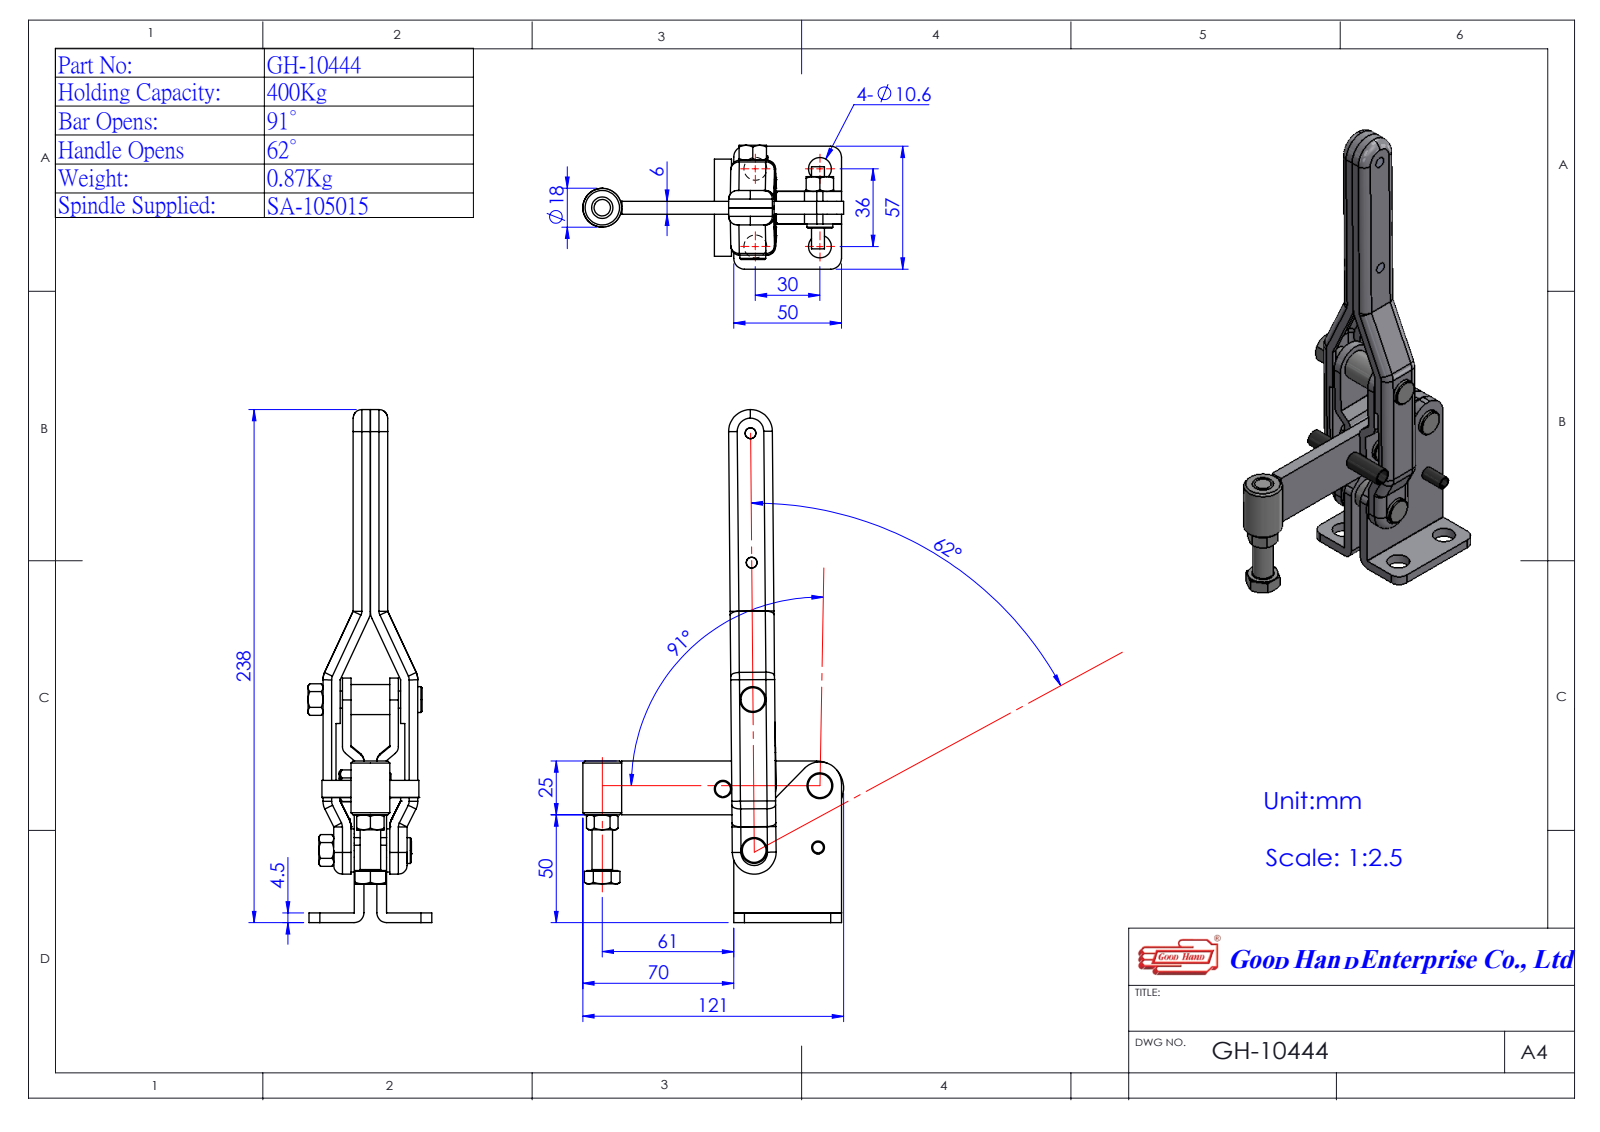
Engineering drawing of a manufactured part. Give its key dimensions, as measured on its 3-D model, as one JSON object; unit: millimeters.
{"part_name": "Group7^GH-10444(簡化); Group6^GH-10444(簡化); GH-10444(簡化); Group2^GH-10444(簡化) (+2 more)", "step_written_by": "SolidWorks 2016 (AUTOMOTIVE_DESIGN)", "units": "millimeters", "bodies": {"solids": 6, "faces": 556, "planar": 261, "cylindrical": 179, "other": 116}, "overall_size": [238.01, 121.25, 57.43], "volume_mm3": 103845, "surface_area_mm2": 69463, "round_holes": [[10.6, 4], [6, 3], [5, 1], [7, 1], [7.94, 1]], "round_bosses_or_shafts": [[9, 4], [6, 3], [20, 1], [18, 1], [12, 1], [10, 1], [8, 1]], "partial_cylinders_radius": [[2, 20], [4, 20], [0.1, 14], [8.1, 8], [5, 5], [2.1, 4], [4.1, 4], [6.1, 4]], "face_to_face_distances": [6, 2, 4.5, 10.5, 15, 14, 12, 16, 1.5, 3], "hole_center_spacings": [30, 36, 46.86, 73.25, 102.59, 14.88, 28.61, 30.2]}
